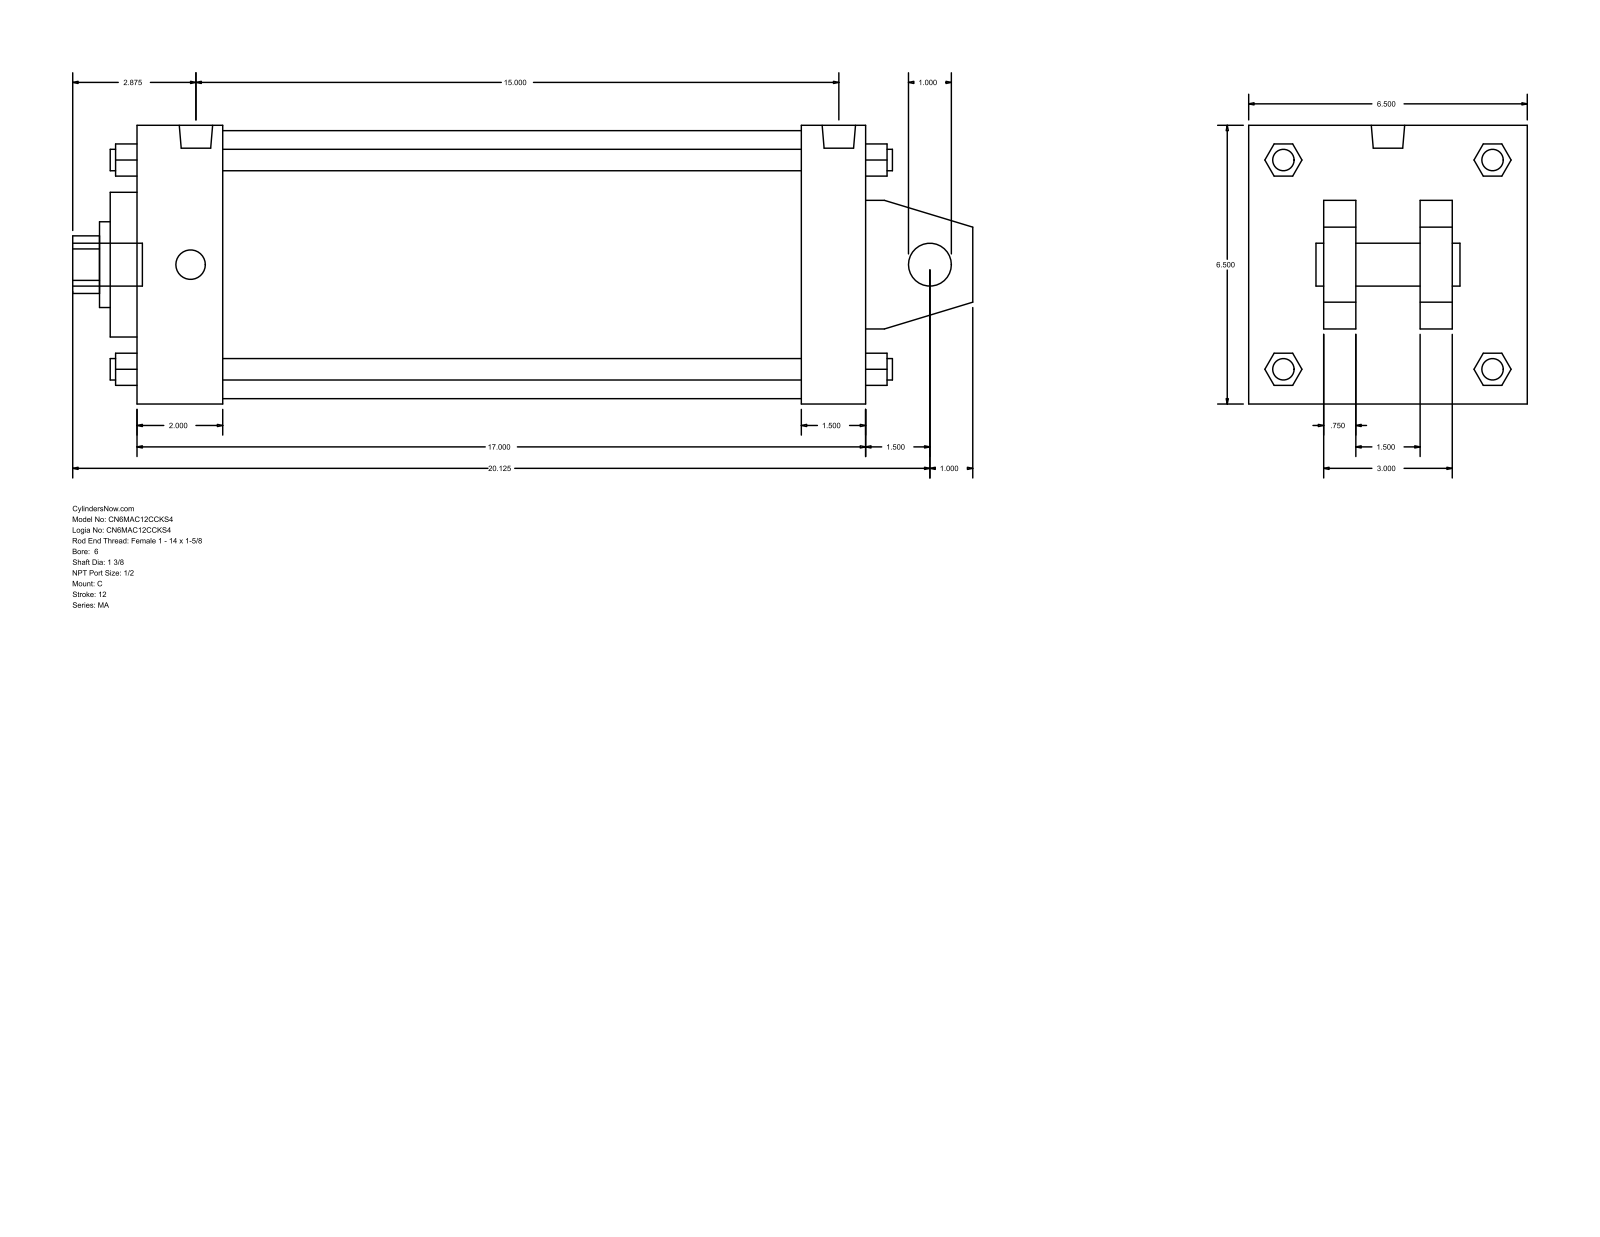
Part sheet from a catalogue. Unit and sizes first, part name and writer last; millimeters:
Units: millimetres
Overall size (bounding box): 533.4 × 165.1 × 165.1
Round holes (diameter × count): ⌀25.4 ×1, ⌀34.92 ×1, ⌀50.8 ×1, ⌀85.72 ×1, ⌀158.75 ×1
Round bosses / shafts (diameter × count): ⌀17.46 ×4, ⌀12.7 ×4, ⌀19.77 ×2, ⌀25.4 ×1
Partial cylindrical surfaces — rounded edges, fillets, slot ends (radius × count): R17.06 ×1
Main face-to-face distances: 165.1, 431.8, 38.1, 19.05, 63.5, 101.6, 50.8, 44.45, 120.65, 393.7
Bodies: 0 solids, 141 faces (109 planar, 32 cylindrical, 0 other)
Part name (STEP PRODUCT): MA_C__0600_1.375
STEP written by: GSSL Pune (CONFIG_CONTROL_DESIGN)
